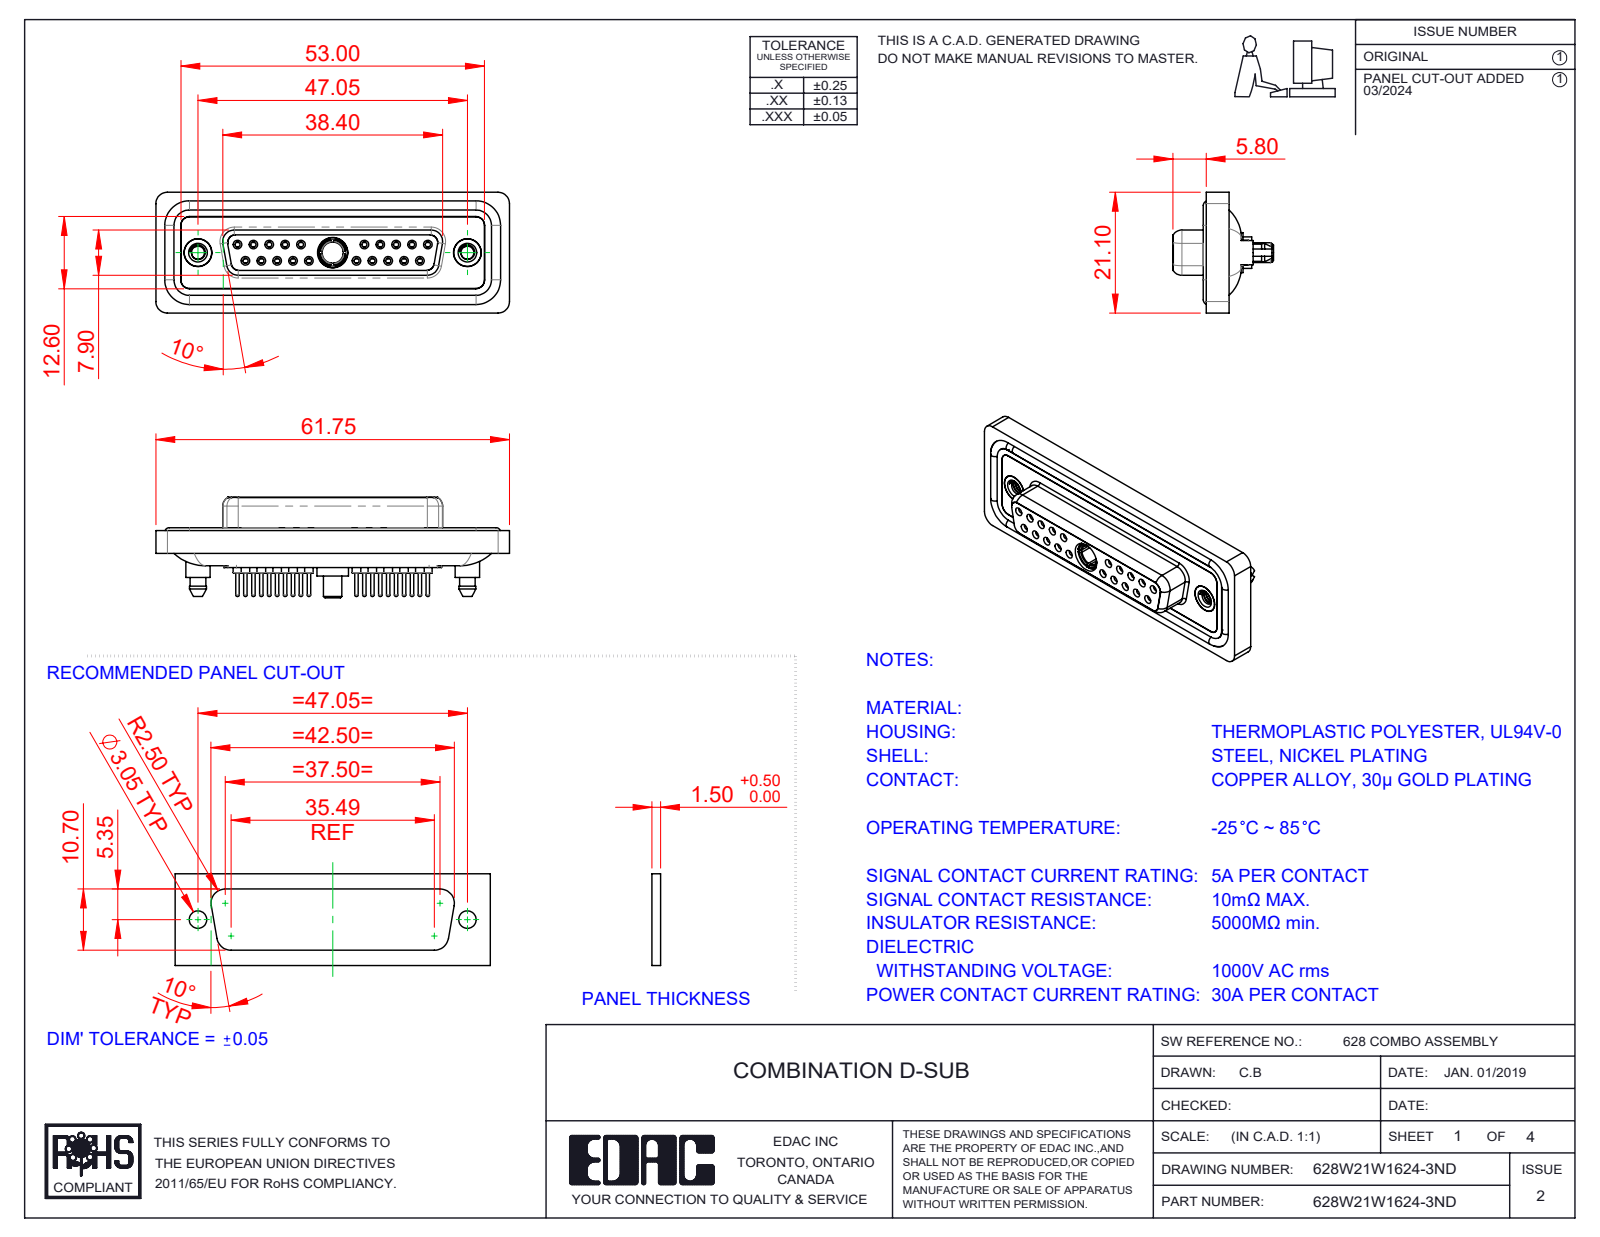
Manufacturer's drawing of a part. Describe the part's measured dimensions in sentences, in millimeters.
The part is named "628Combo Shell Front_25 Contacts; Power Socket_30A S; 628Combo Shell Rear_25 Contacts; 628W21W1624-3ND (+5 more)". Its 3-D file was written by "SolidWorks 2023 (CONFIG_CONTROL_DESIGN)". It is 29 solids with 1626 faces: 450 planar, 639 cylindrical and 537 other. Overall it measures 61.75 by 21.1 by 17.55 millimeters. Its volume is 8 517 cubic millimeters and its surface area 14 346 square millimeters. Round holes: 20 of diameter 0.9, 20 of diameter 1.1, 20 of diameter 1.5, 20 of diameter 2, 10 of diameter 1.6, 10 of diameter 1.7, 3 of diameter 4.85, 2 of diameter 2.26, 2 of diameter 4, 2 of diameter 4.05, 2 of diameter 5, 1 of diameter 3.7. Round bosses or shafts: 20 of diameter 2.2, 20 of diameter 0.6, 14 of diameter 1.6, 2 of diameter 5.4, 2 of diameter 4.95, 2 of diameter 4.8, 2 of diameter 4.25, 1 of diameter 5.5. Partial cylindrical surfaces (rounded edges, fillets, slot ends): 24 of radius 1.5, 18 of radius 2, 10 of radius 1.6, 8 of radius 1.35, 4 of radius 0.25, 4 of radius 0.5, 4 of radius 0.6, 4 of radius 0.65. The main face-to-face distances are 0.4, 1.8, 7.45, 6.6, 5.65, 1.6, 0.5, 7.05, 2.9, 1.1. The hole center spacings are 3.16, 2.77, 5.54, 5.03, 8.31, 7.48, 16.62, 19.39.
